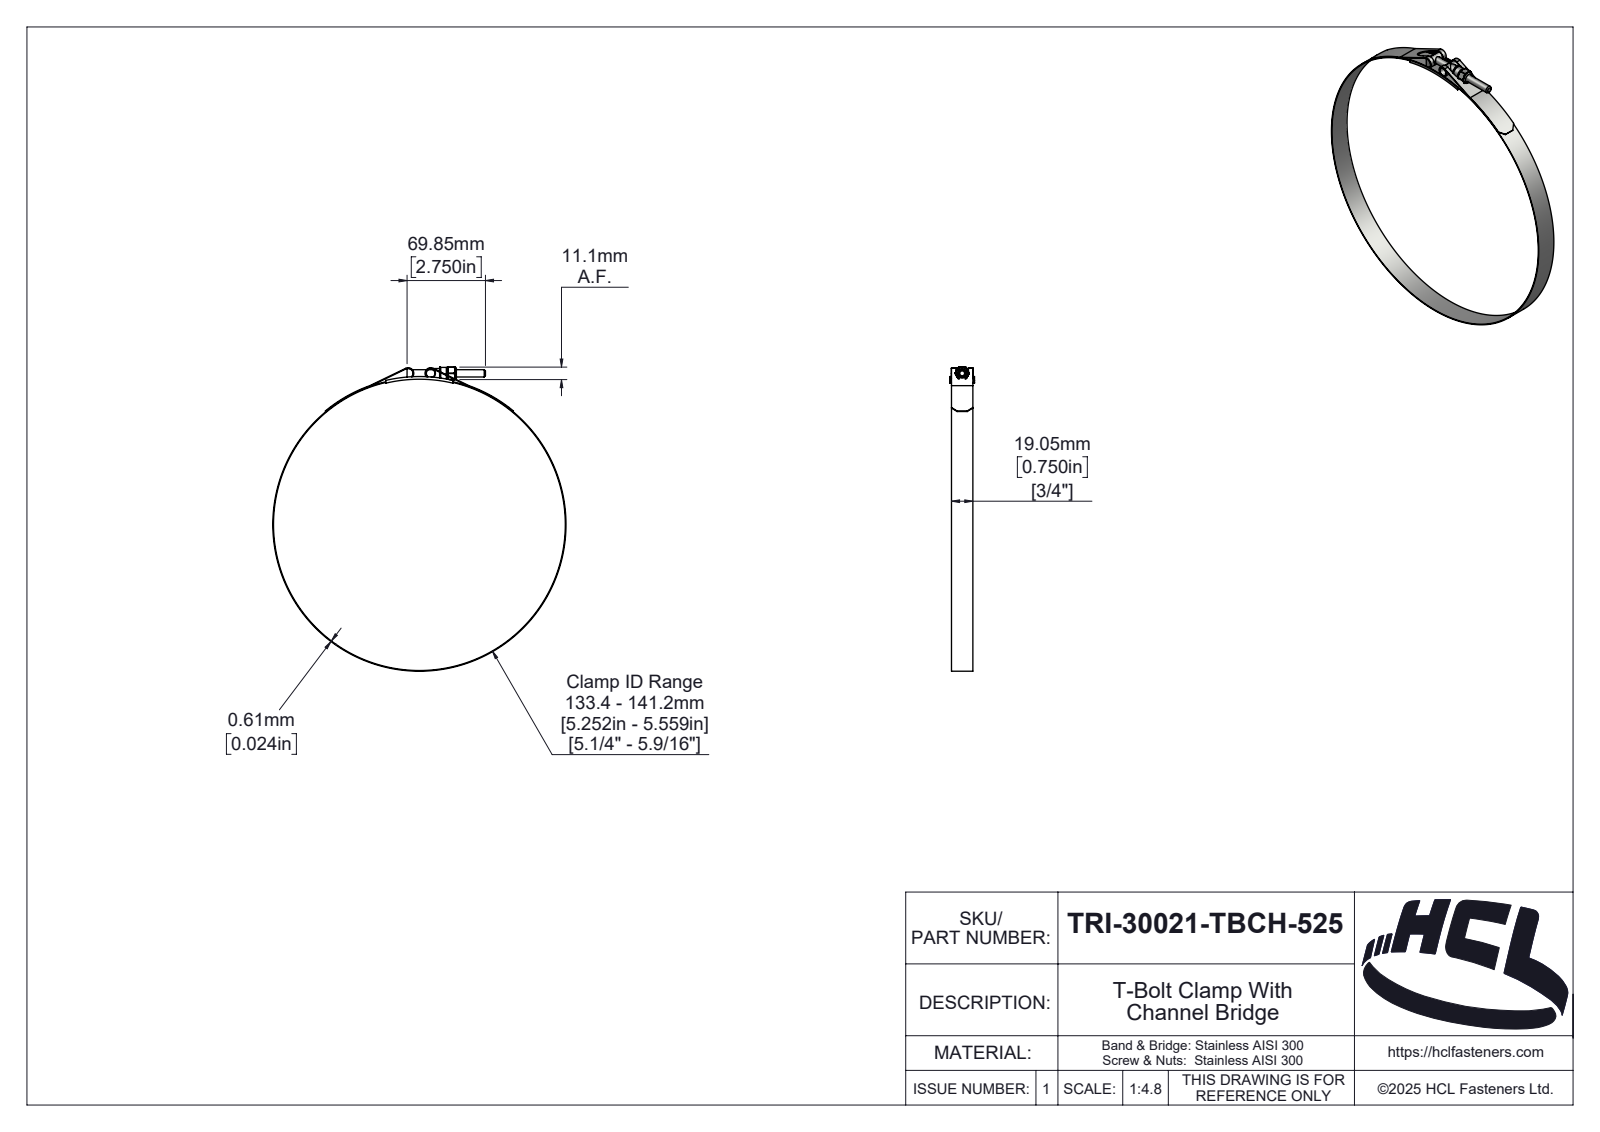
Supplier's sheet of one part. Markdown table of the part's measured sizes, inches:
| quantity | value |
| --- | --- |
| part name | TRI-30021-TBCH-525 |
| STEP written by | SolidWorks 2025 (AUTOMOTIVE_DESIGN) |
| units | inches |
| bodies | 6 solids, 330 faces (46 planar, 122 cylindrical, 162 other) |
| overall size | 10.668 × 10.284 × 0.866 |
| volume | 0.99 in³ |
| surface area | 70.17 in² |
| round holes (diameter × count) | 0.213 × 1, 0.25 × 1, 0.256 × 1, 0.298 × 1, 10.236 × 1 |
| round bosses / shafts (diameter × count) | 0.338 × 2, 10.284 × 1, 0.417 × 1 |
| partial cylindrical surfaces (radius × count) | 0.015 × 6, 0.02 × 2, 0.173 × 2, 0.197 × 2, 0.023 × 1, 0.095 × 1, 0.119 × 1, 0.126 × 1 |
| main face-to-face distances | 0.024, 0.75, 0.058, 0.808, 0.842, 0.034, 0.784, 0.029, 0.866, 0.818 |
| hole center spacings | 5.315 |
